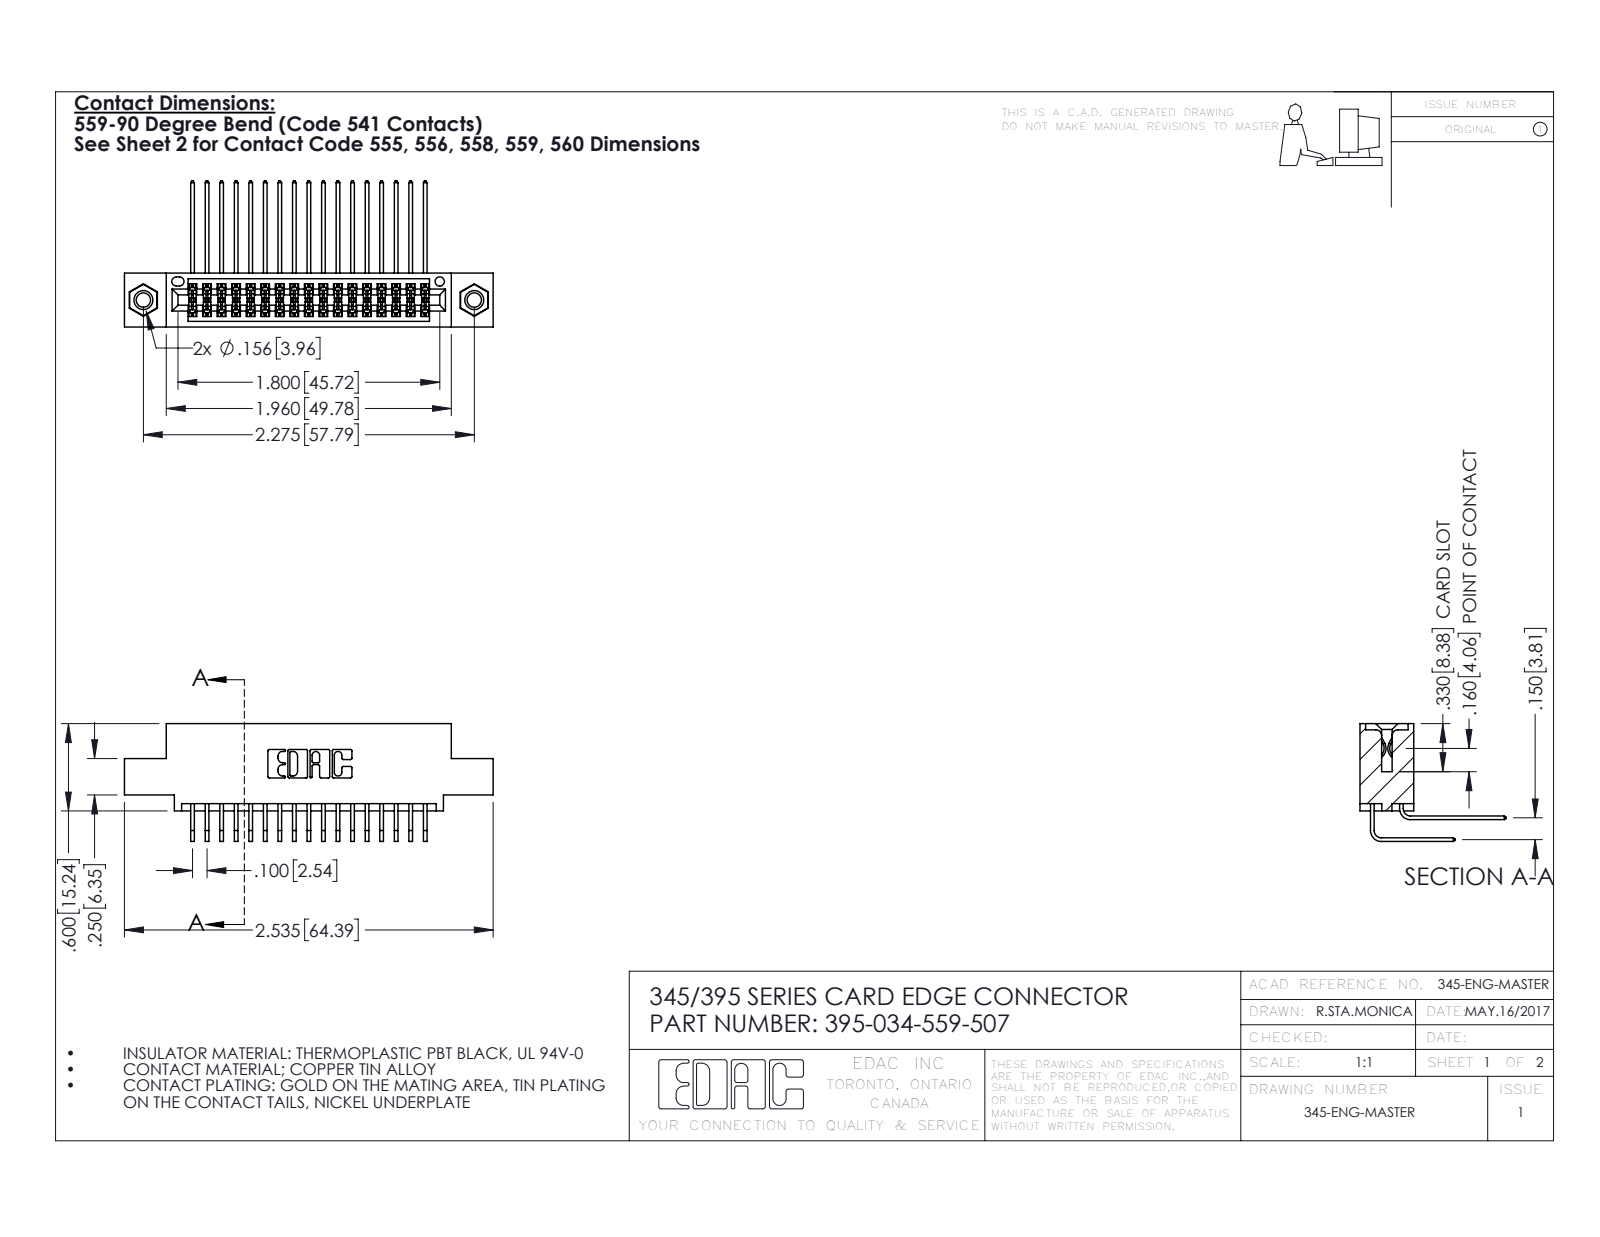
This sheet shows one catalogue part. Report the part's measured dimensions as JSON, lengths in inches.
{"part_name": "345-292-001_559 Tail - 2; 345 Part_0.110 Offset - 0.156 Dia-TI; 345-292-001_558 559 Tail - 1; 345-250-001_345-250-005-103 (+1 more)", "step_written_by": "SolidWorks 2016 (CONFIG_CONTROL_DESIGN)", "units": "inches", "bodies": {"solids": 37, "faces": 1958, "planar": 1306, "cylindrical": 636, "other": 16}, "overall_size": [2.535, 1.005, 0.809], "volume_in3": 0.374, "surface_area_in2": 14.92, "round_holes": [[0.098, 2], [0.125, 2], [0.156, 2], [0.064, 1]], "round_bosses_or_shafts": [[0.155, 2]], "partial_cylinders_radius": [[0.006, 52], [0.01, 22], [0.007, 6], [0.031, 6], [0.026, 3], [0.014, 2], [0.019, 2], [0.022, 2]], "face_to_face_distances": [0.072, 0.298, 0.2, 0.37, 0.098, 0.272, 0.025, 0.225, 0.15, 0.175], "hole_center_spacings": [0.27, 2.041, 2.275]}
